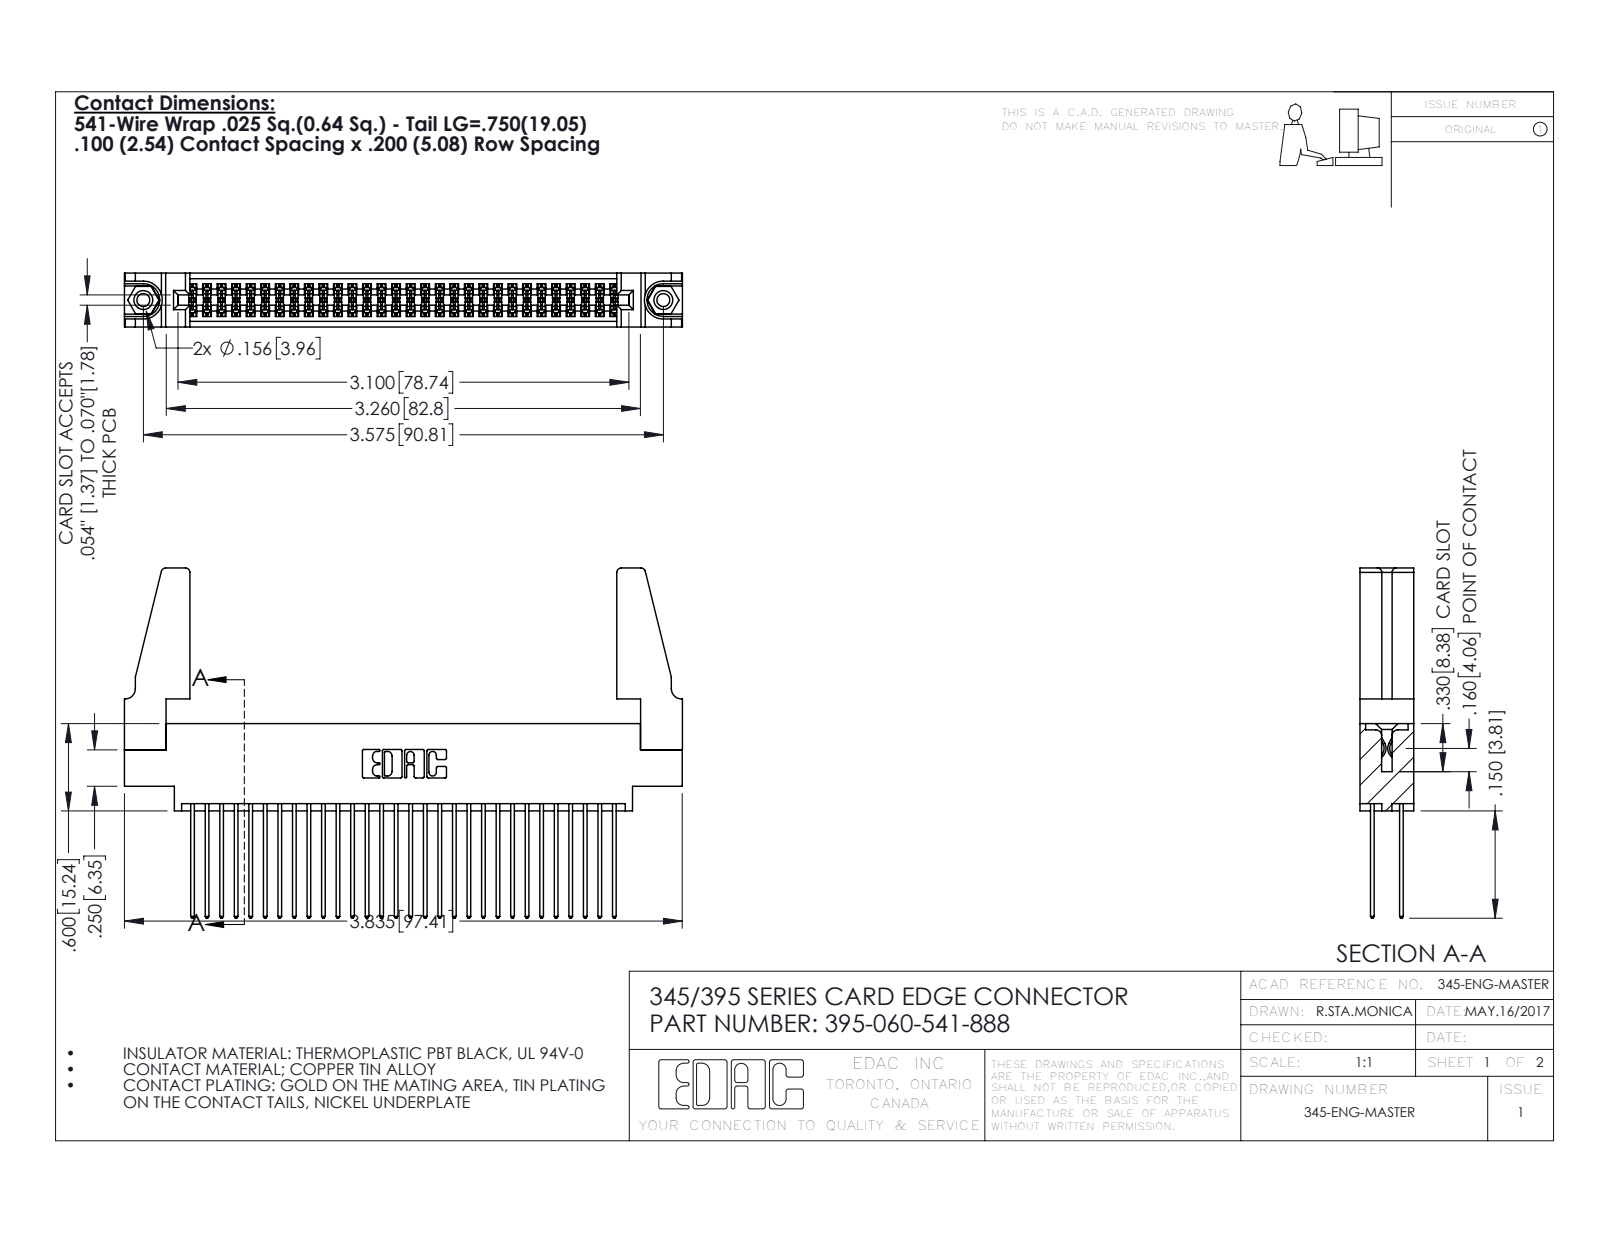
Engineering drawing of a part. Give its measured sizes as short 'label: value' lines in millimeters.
name: 395-060-541-888; 345-220-078_345-220-088; 345 Part_0.170 Offset - 0.156 Dia-TH; 345-250-001_345-250-001-102 (+1 more)
written by: SolidWorks 2016 (CONFIG_CONTROL_DESIGN)
unit: mm
bodies: 65 solids, 3254 faces (2136 planar, 1102 cylindrical, 16 other)
size: 97.4 × 61.1 × 9.4
volume: 12 800 mm³; area: 18 820 mm²
holes: 2× ⌀2.3, 2× ⌀3.2, 2× ⌀4, 1× ⌀1.6
bosses: 2× ⌀3.9
rounds: 90× R0.2, 60× R0.3, 22× R0.3, 8× R0.8, 6× R0.2, 6× R0.8, 3× R0.7, 2× R0.4
face distances: 1.8, 7.6, 9.4, 5.1, 2.5, 6.9, 0.6, 5.7, 4.4, 3.8
hole spacings: 6.9, 84.8, 90.8
